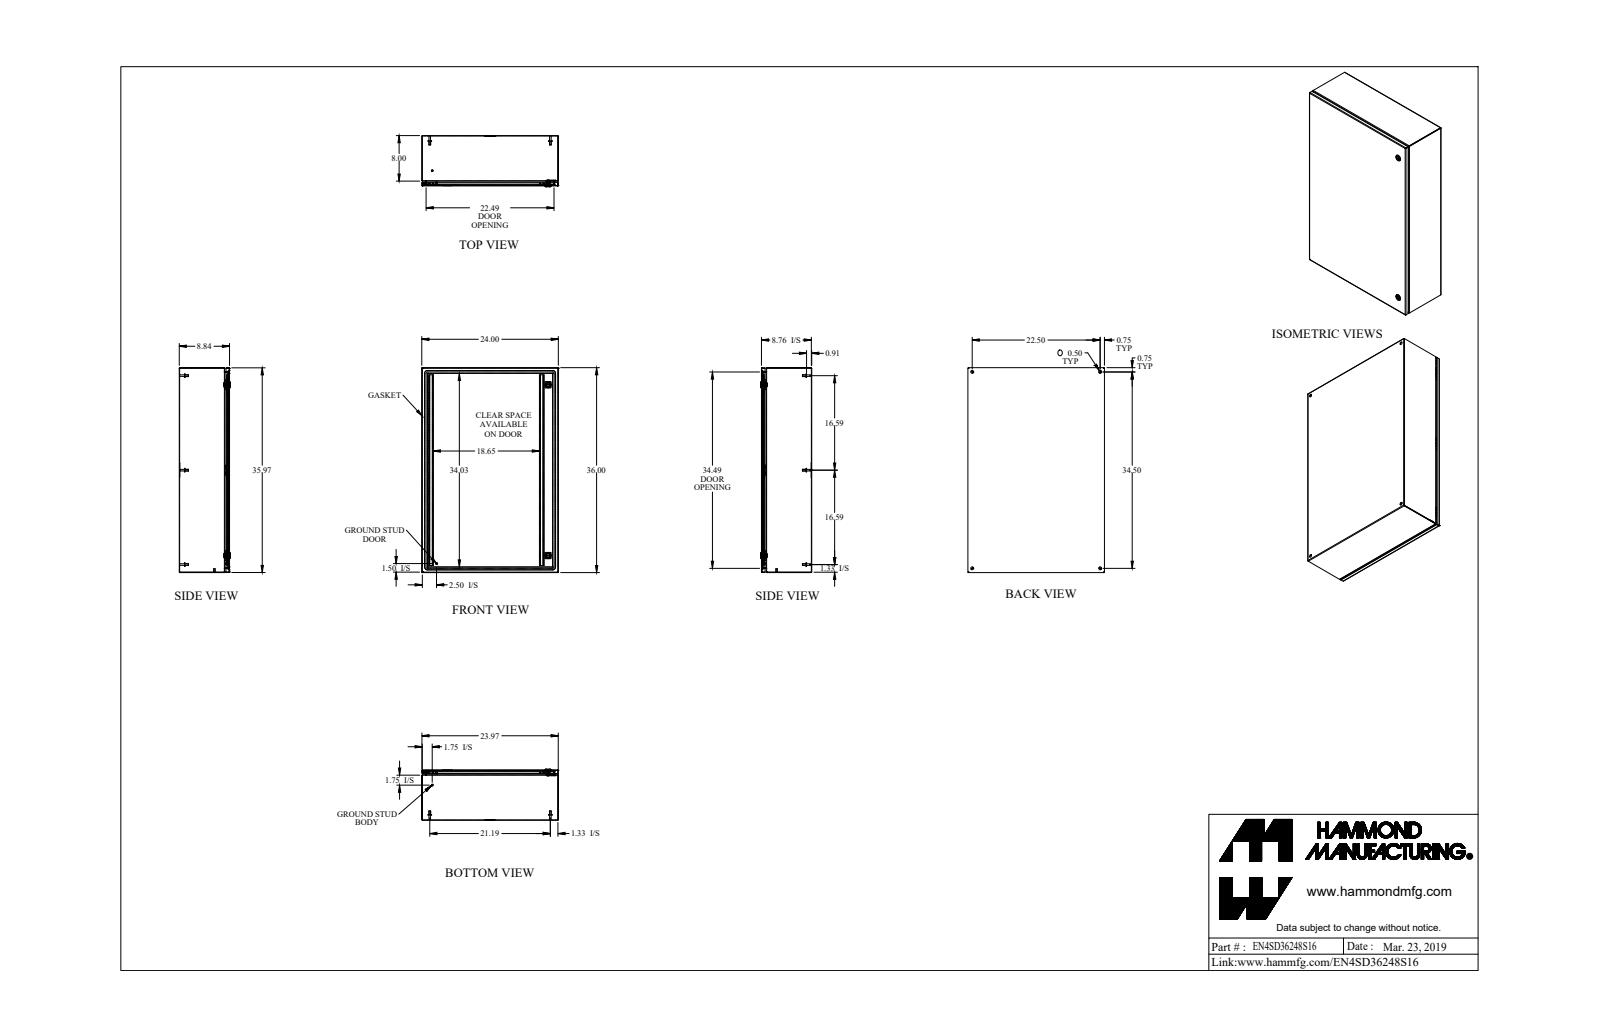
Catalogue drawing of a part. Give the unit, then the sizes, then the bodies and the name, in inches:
Units: inches
Overall size (bounding box): 36 × 24 × 9.002
Round holes (diameter × count): ⌀0.5 ×6, ⌀0.197 ×2, ⌀0.387 ×2, ⌀0.63 ×2, ⌀0.768 ×2, ⌀0.172 ×1, ⌀0.24 ×1, ⌀0.242 ×1
Round bosses / shafts (diameter × count): ⌀0.625 ×8, ⌀0.313 ×8, ⌀0.275 ×6, ⌀1.1 ×2, ⌀0.785 ×2, ⌀0.525 ×2, ⌀0.25 ×2, ⌀0.236 ×2
Partial cylindrical surfaces — rounded edges, fillets, slot ends (radius × count): R0.036 ×20, R0.108 ×20, R0.25 ×16, R0.01 ×12, R0.048 ×12, R0.006 ×6, R0.062 ×6, R0.125 ×4
Main face-to-face distances: 0.072, 8.77, 8.698, 8.842, 23.928, 35.928, 23.856, 24, 35.856, 36
Hole centre spacings: 21.557, 22.5, 34.5, 41.189, 2.487, 2.488, 30, 32.267
Volume: 226.9 in³ · Surface area: 6 381 in²
Bodies: 35 solids, 958 faces (458 planar, 312 cylindrical, 188 other)
Part name (STEP PRODUCT): EN4SD36248S16_Default
STEP written by: SolidWorks 2019 (CONFIG_CONTROL_DESIGN)
